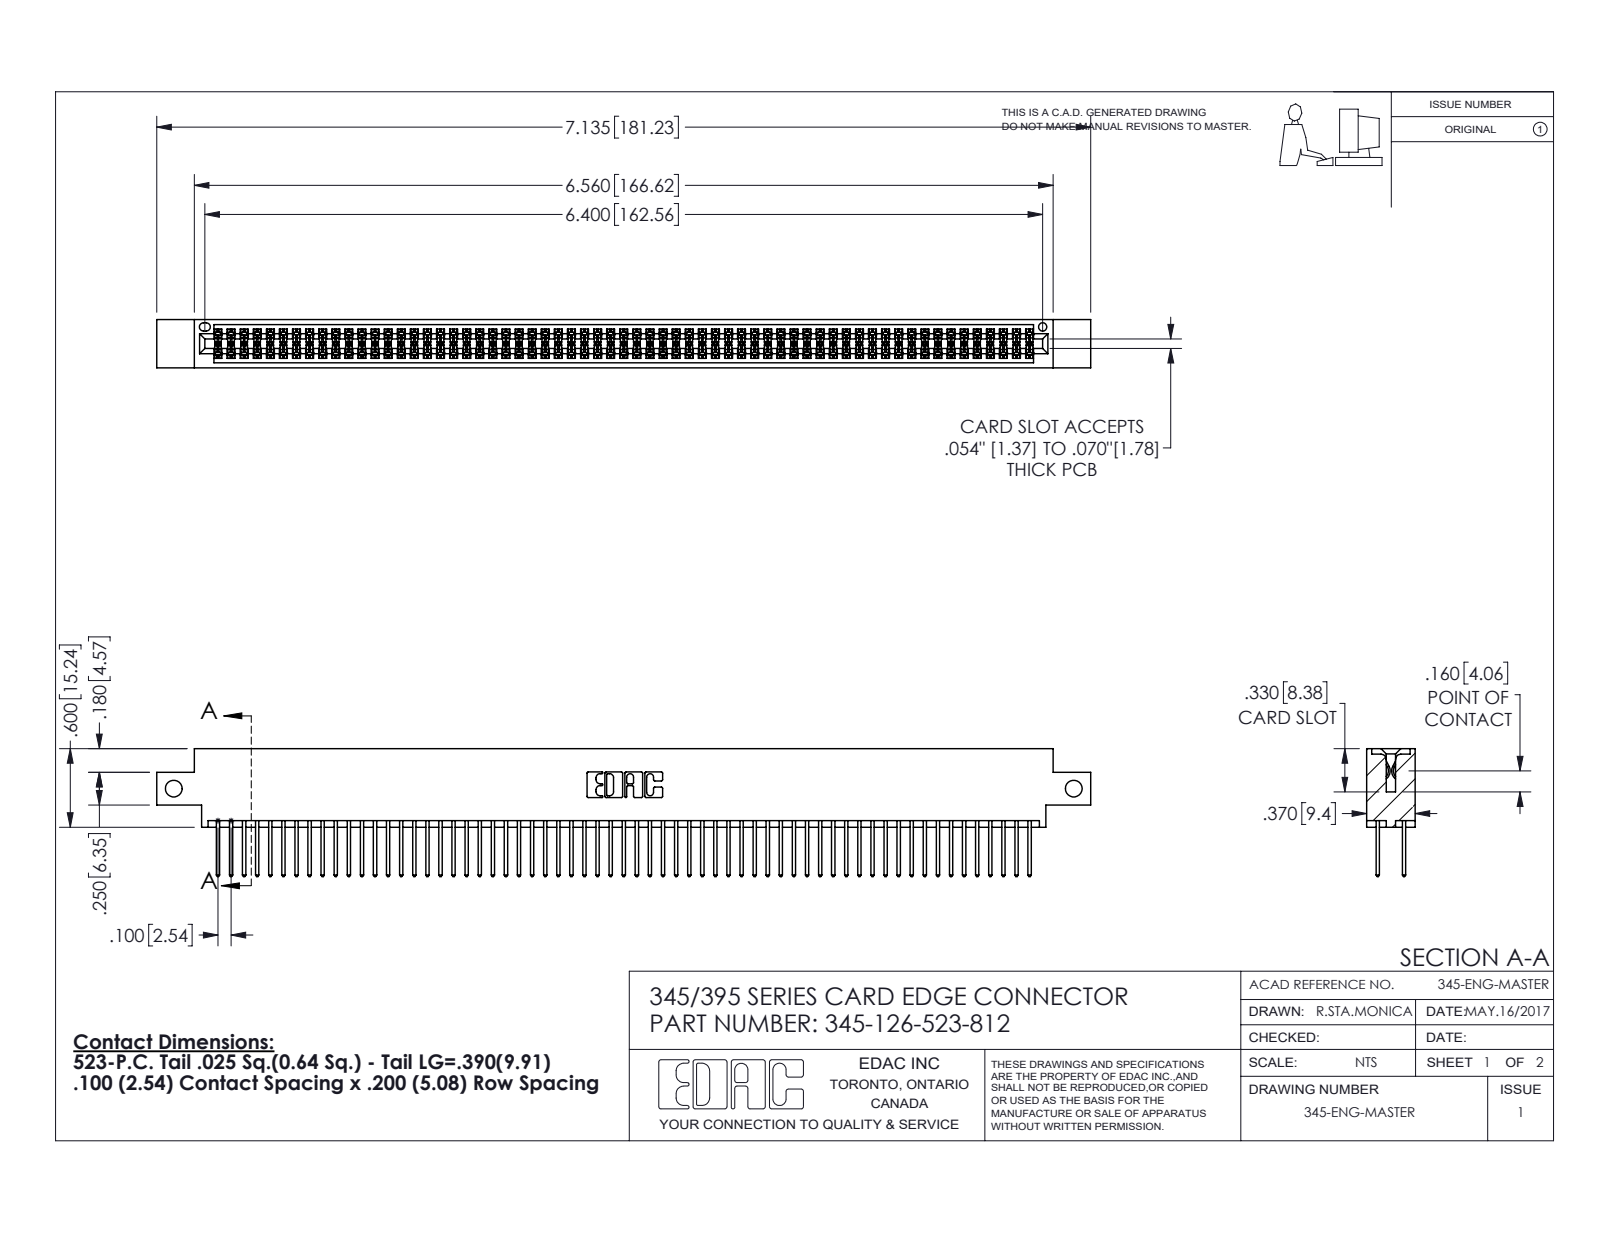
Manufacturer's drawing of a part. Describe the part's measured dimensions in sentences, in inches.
The part is named "345-292-001_345-293-123; 345-126-523-812; 345 Part_0.170 Offset - Side Mount". Its 3-D file was written by "SolidWorks 2016 (CONFIG_CONTROL_DESIGN)". It is 127 solids with 6430 faces: 4242 planar, 2188 cylindrical and 0 other. Overall it measures 7.135 by 0.977 by 0.37 inches. Its volume is 1.09 cubic inches and its surface area 43.35 square inches. Round holes: 2 of diameter 0.128, 1 of diameter 0.064. Partial cylindrical surfaces (rounded edges, fillets, slot ends): 189 of radius 0.006, 126 of radius 0.01, 22 of radius 0.01, 6 of radius 0.007, 6 of radius 0.031, 3 of radius 0.026, 2 of radius 0.014, 2 of radius 0.019. The main face-to-face distances are 0.298, 0.072, 0.2, 0.098, 0.272, 0.025, 0.37, 0.225, 0.175, 0.149. The hole center spacings are 6.875.
